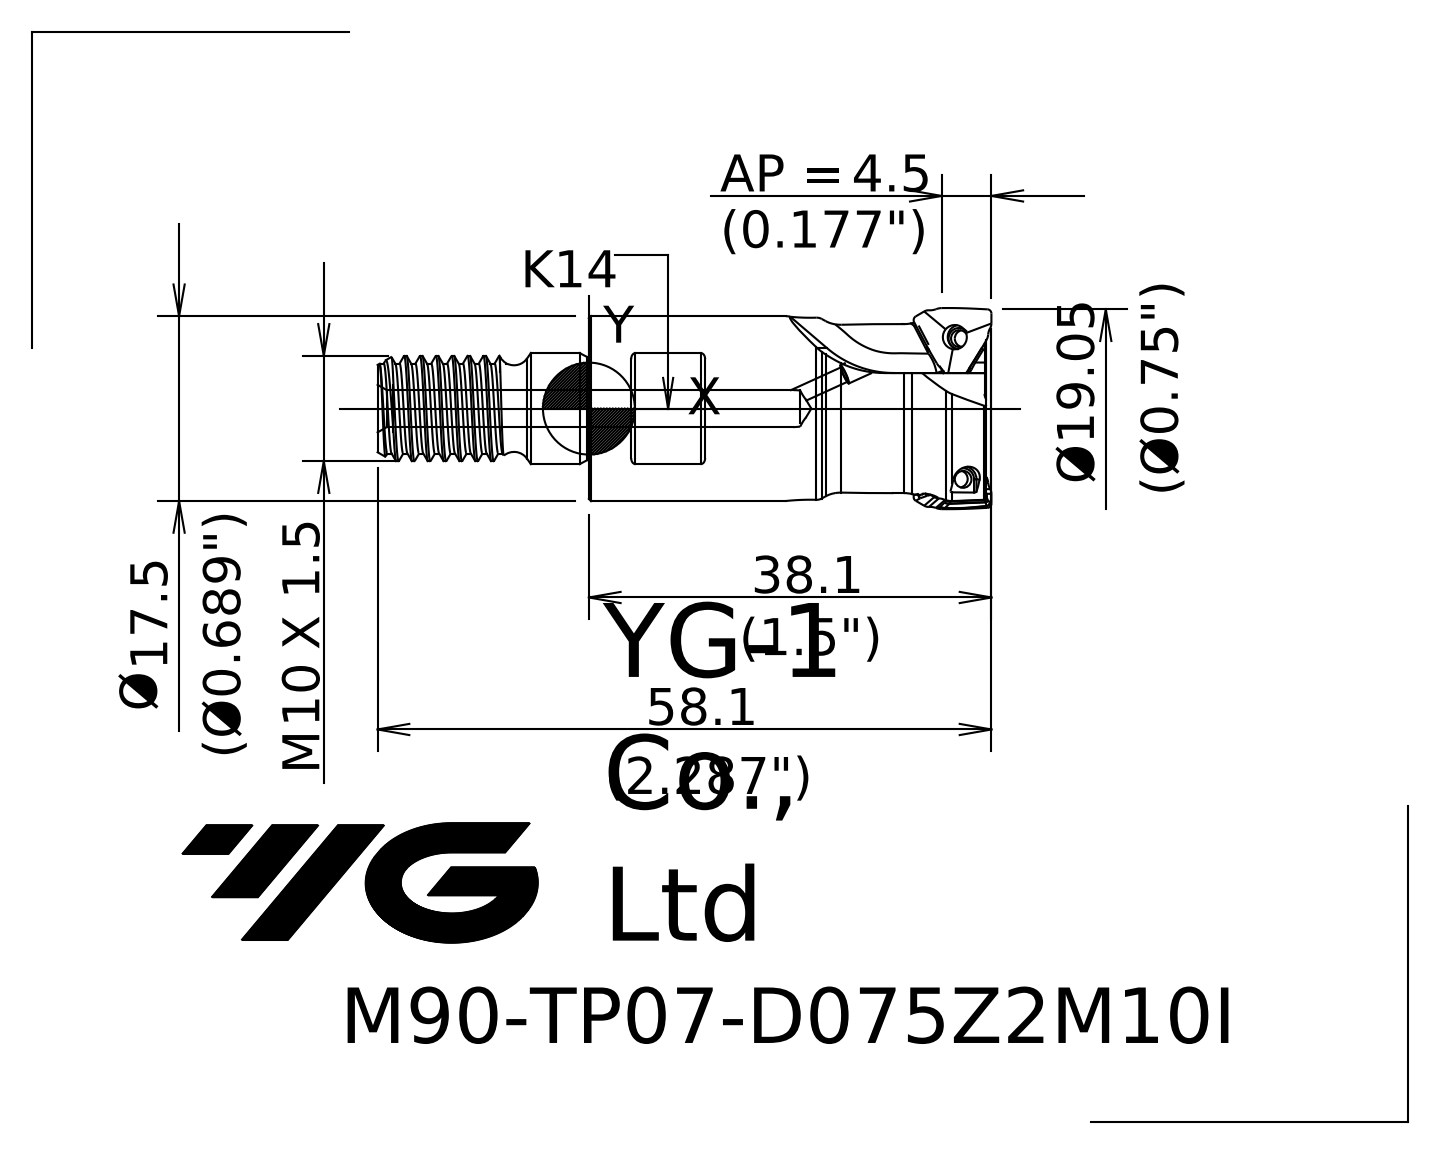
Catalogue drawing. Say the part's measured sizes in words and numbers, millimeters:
The part is named "102268184FE00rqu". Its 3-D file was written by "SIEMENS PLM Software NX 10.0 (AP203_CONFIGURATION_CONTROLLED_3D_DESIGN_OF_MECHANICAL_PARTS_AND_ASSEMBLIES_MIM_LF)". It is 1 solid with 69 faces: 12 planar, 11 cylindrical and 46 other. Overall it measures 58.1 by 19.09 by 19.09 millimeters. Its volume is 9 497 cubic millimeters and its surface area 4 759 square millimeters. Round holes: 1 of diameter 1.5, 1 of diameter 3.5. Round bosses or shafts: 1 of diameter 17.5, 1 of diameter 16, 1 of diameter 10.5, 1 of diameter 10, 1 of diameter 8.5. Partial cylindrical surfaces (rounded edges, fillets, slot ends): 4 of radius 0.4. The main face-to-face distances are 37.45, 14, 57.45, 20, 37.6, 57.6, 26.6, 26.45, 11, 31.
